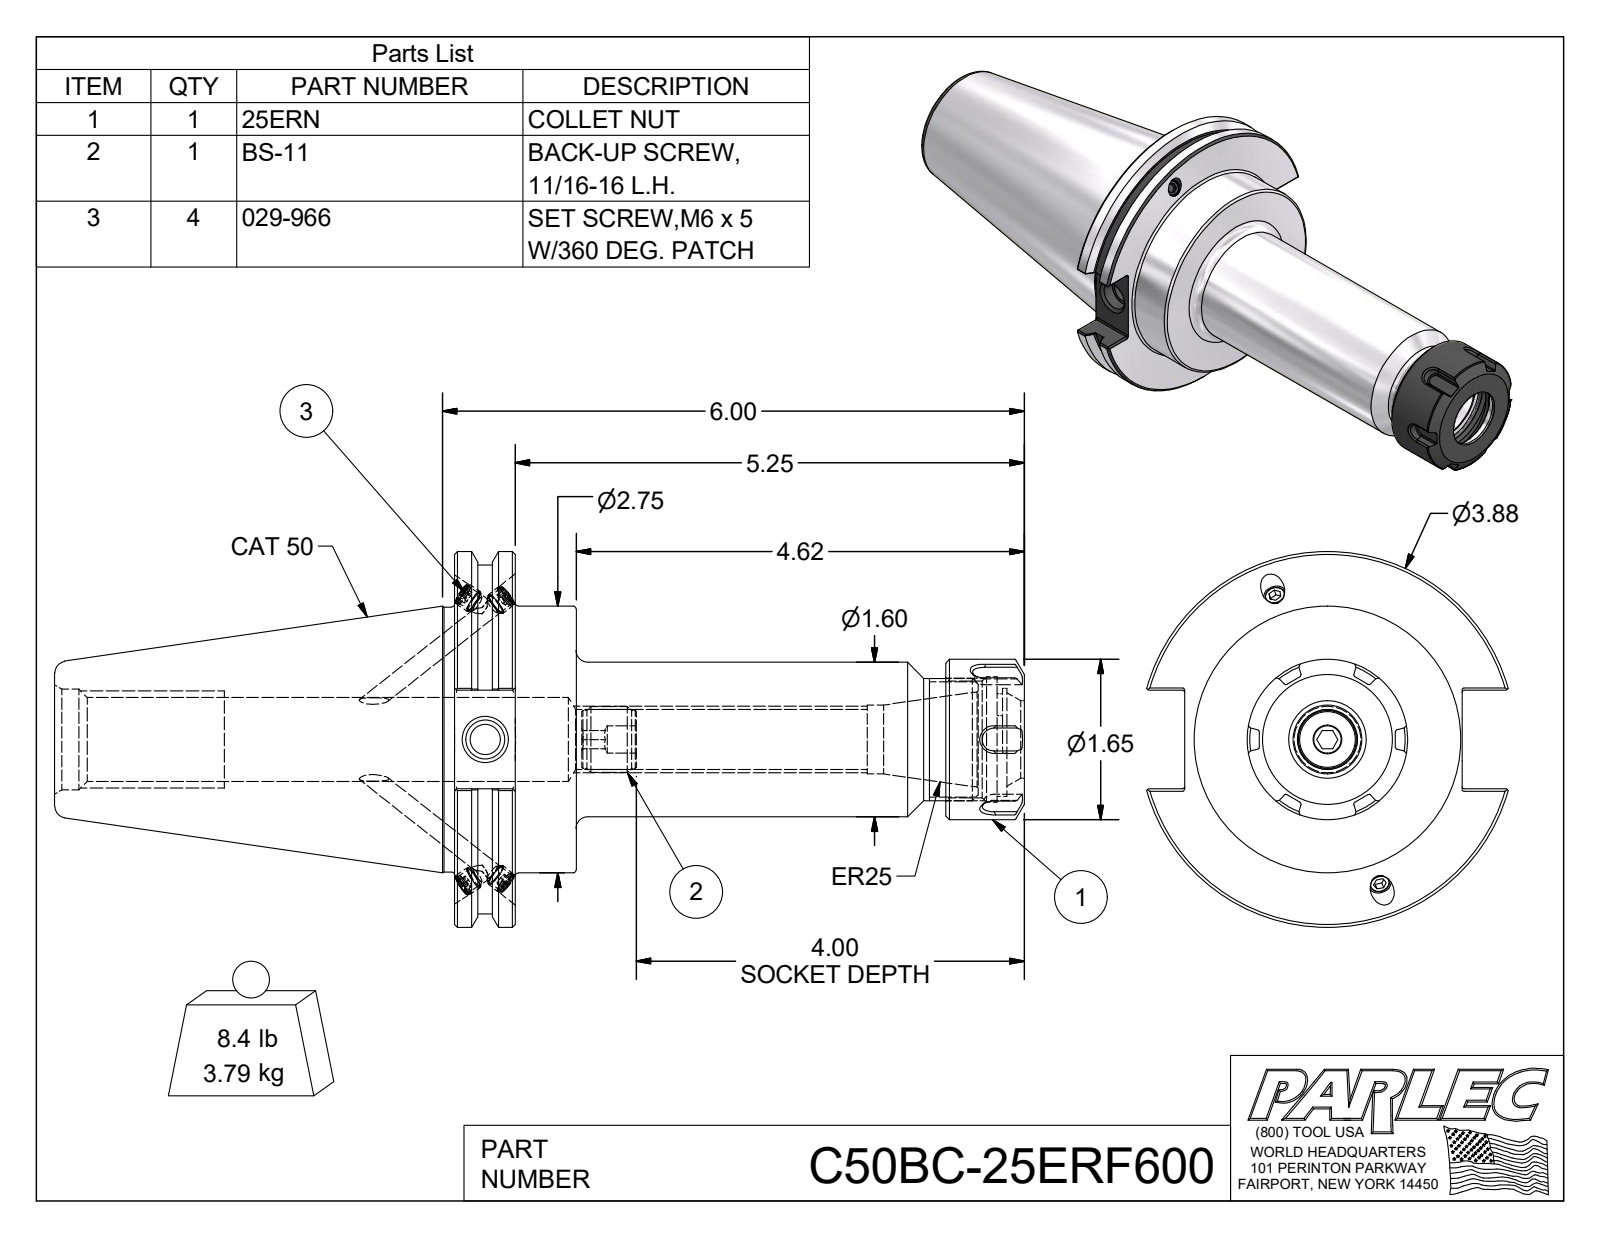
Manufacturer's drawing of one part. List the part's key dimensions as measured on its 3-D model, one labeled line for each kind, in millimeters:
Part name (STEP PRODUCT): C50BCB-25ER6-1; 029-966; 25ERN; BS-11 (+1 more)
STEP written by: Autodesk Inventor 2016 (AUTOMOTIVE_DESIGN)
Units: millimetres
Bodies: 7 solids, 275 faces (120 planar, 71 cylindrical, 84 other)
Overall size (bounding box): 254 × 98.42 × 94.71
Volume: 489 950 mm³ · Surface area: 76 839 mm²
Round holes (diameter × count): ⌀5 ×4, ⌀6.1 ×4, ⌀7.11 ×1, ⌀8 ×1, ⌀10.13 ×1, ⌀15.75 ×1, ⌀18.03 ×1, ⌀20.32 ×1, ⌀21.97 ×1, ⌀26.37 ×1, ⌀30.5 ×1, ⌀32.88 ×1
Round bosses / shafts (diameter × count): ⌀6.2 ×4, ⌀6 ×4, ⌀98.42 ×1, ⌀91.29 ×1, ⌀69.85 ×1, ⌀69.34 ×1, ⌀42 ×1, ⌀40.51 ×1
Partial cylindrical surfaces — rounded edges, fillets, slot ends (radius × count): R0.51 ×24, R12 ×1, R13.06 ×1, R13.43 ×1
Main face-to-face distances: 15.88, 31.88, 16, 149.23, 133.35, 117.35, 128.66, 112.78, 96.78, 20.57
